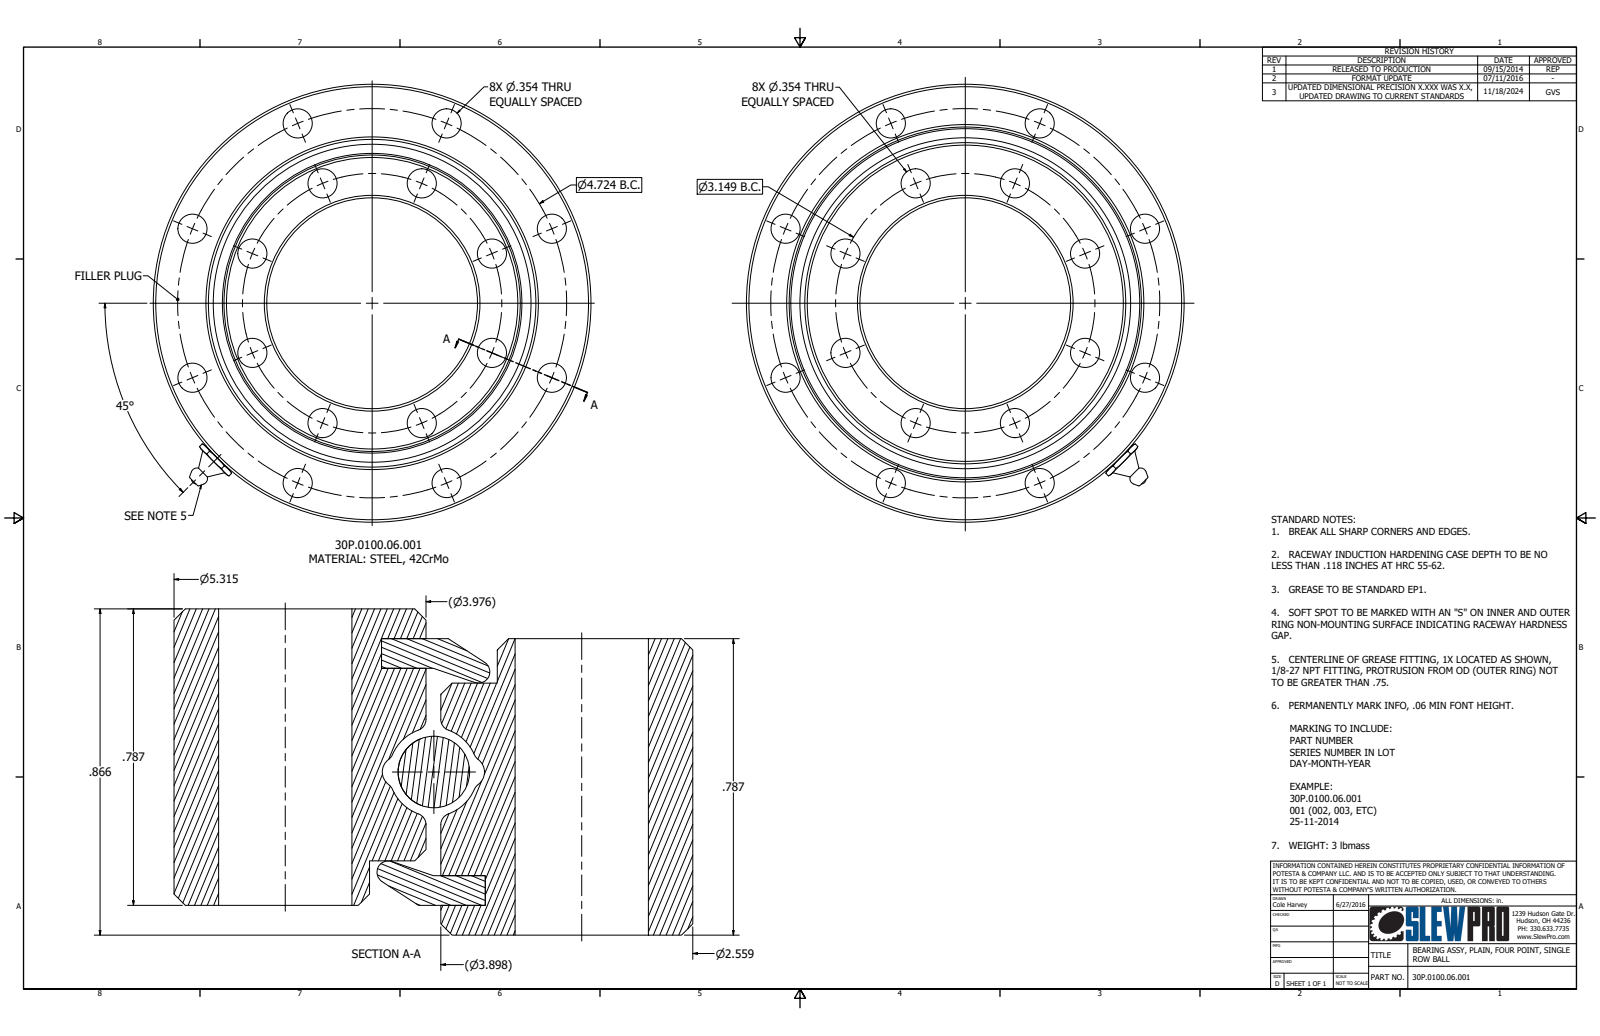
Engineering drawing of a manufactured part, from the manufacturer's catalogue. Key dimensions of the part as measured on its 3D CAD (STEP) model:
Part name (STEP PRODUCT): 30P.0100.06.001; 1_8 NPT Fitting
STEP written by: Autodesk Inventor 2024 (AUTOMOTIVE_DESIGN)
Units: inches
Bodies: 94 solids, 292 faces (25 planar, 37 cylindrical, 230 other)
Overall size (bounding box): 5.315 × 5.315 × 0.866
Volume: 11.62 in³ · Surface area: 123.7 in²
Round holes (diameter × count): ⌀0.354 ×16, ⌀0.1 ×1, ⌀0.336 ×1, ⌀2.559 ×1, ⌀3.661 ×1, ⌀3.976 ×1, ⌀4.213 ×1, ⌀4.276 ×1
Round bosses / shafts (diameter × count): ⌀5.315 ×1, ⌀3.898 ×1, ⌀3.598 ×1
Main face-to-face distances: 0.787, 0.079, 0.708, 0.158, 0.708, 0.079, 0.629, 0.866, 0.55, 0.197
Hole centre spacings: 0.787, 1.574, 1.673, 1.673, 1.808, 2.227, 2.362, 2.839
